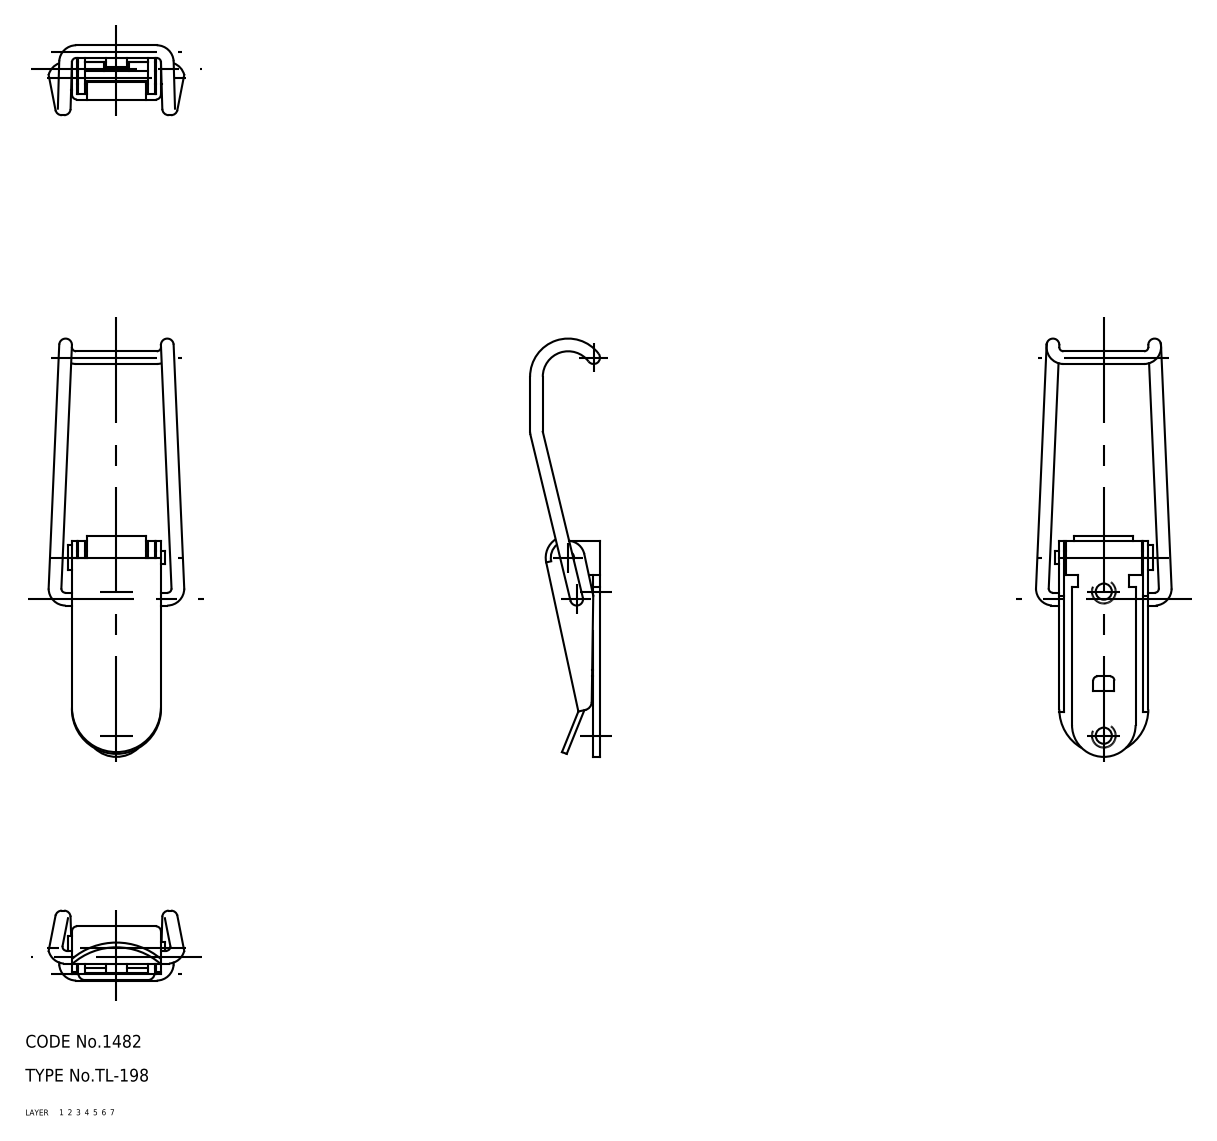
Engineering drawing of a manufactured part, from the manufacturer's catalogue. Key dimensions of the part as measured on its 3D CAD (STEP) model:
Part name (STEP PRODUCT): arm; shaft; lever; base (+1 more)
STEP written by: CADfix (AUTOMOTIVE_DESIGN)
Units: millimetres
Bodies: 4 solids, 120 faces (0 planar, 0 cylindrical, 120 other)
Overall size (bounding box): 98.71 × 32.01 × 16.5
Volume: 4 610 mm³ · Surface area: 7 302 mm²
